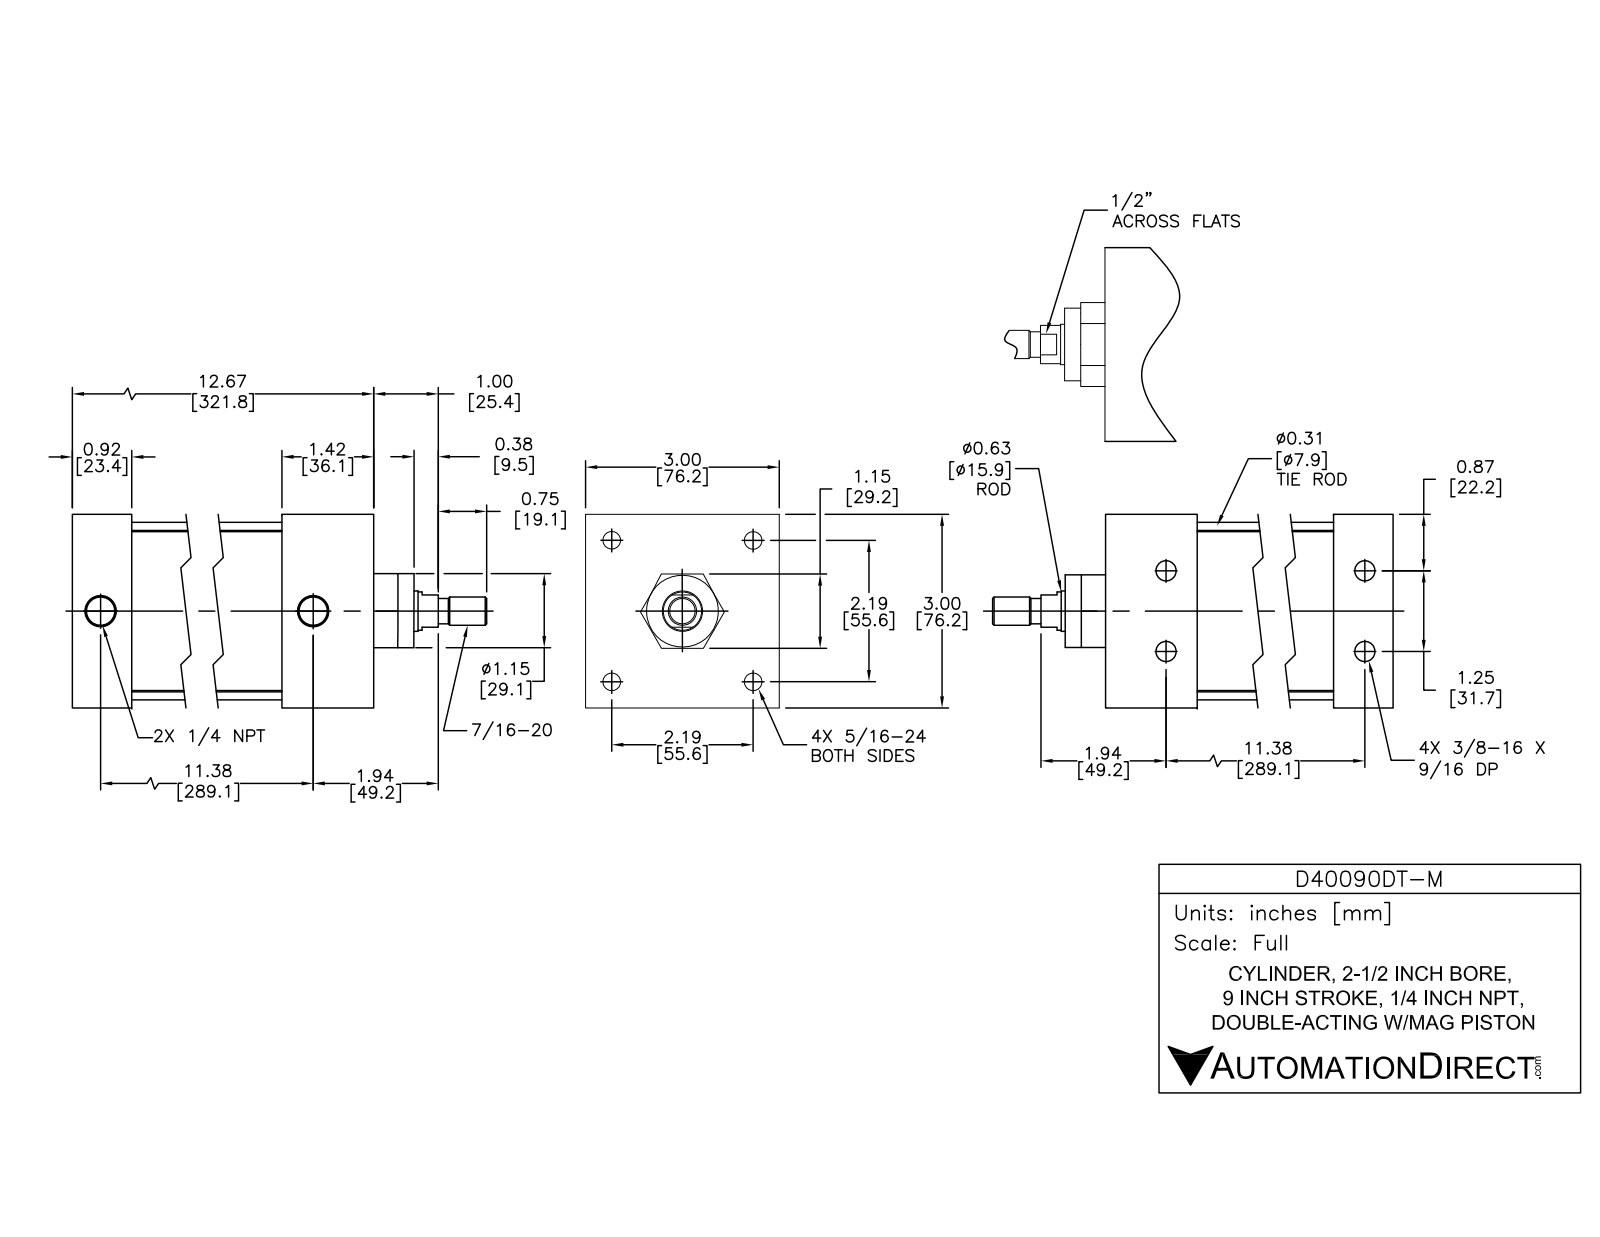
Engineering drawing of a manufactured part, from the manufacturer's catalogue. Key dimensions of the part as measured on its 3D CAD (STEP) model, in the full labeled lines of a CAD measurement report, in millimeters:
Part name (STEP PRODUCT): D40090DT-M PISTON; D40090DT-M; D40090DT-M BODY
STEP written by: SolidWorks 2015 (AUTOMOTIVE_DESIGN)
Units: millimetres
Bodies: 12 solids, 298 faces (94 planar, 114 cylindrical, 90 other)
Overall size (bounding box): 368.2 × 76.2 × 76.2
Volume: 712 300 mm³ · Surface area: 226 200 mm²
Round holes (diameter × count): ⌀6.8 ×4, ⌀7.8 ×4, ⌀9.1 ×4, ⌀12.7 ×4, ⌀7.5 ×2, ⌀12.1 ×2, ⌀15.9 ×1, ⌀16 ×1, ⌀63.5 ×1
Round bosses / shafts (diameter × count): ⌀12.3 ×4, ⌀8 ×4, ⌀7.2 ×4, ⌀69.9 ×1, ⌀63.4 ×1, ⌀28.4 ×1, ⌀15.8 ×1, ⌀15 ×1
Partial cylindrical surfaces — rounded edges, fillets, slot ends (radius × count): R7.6 ×4
Main face-to-face distances: 76.2, 2, 262.3, 323.7, 297.8, 25.9, 36.1, 261.8, 287.7, 25.4
Hole centre spacings: 39.5, 55.9, 289.2, 288.8, 15.9, 15.9, 31.8, 79
